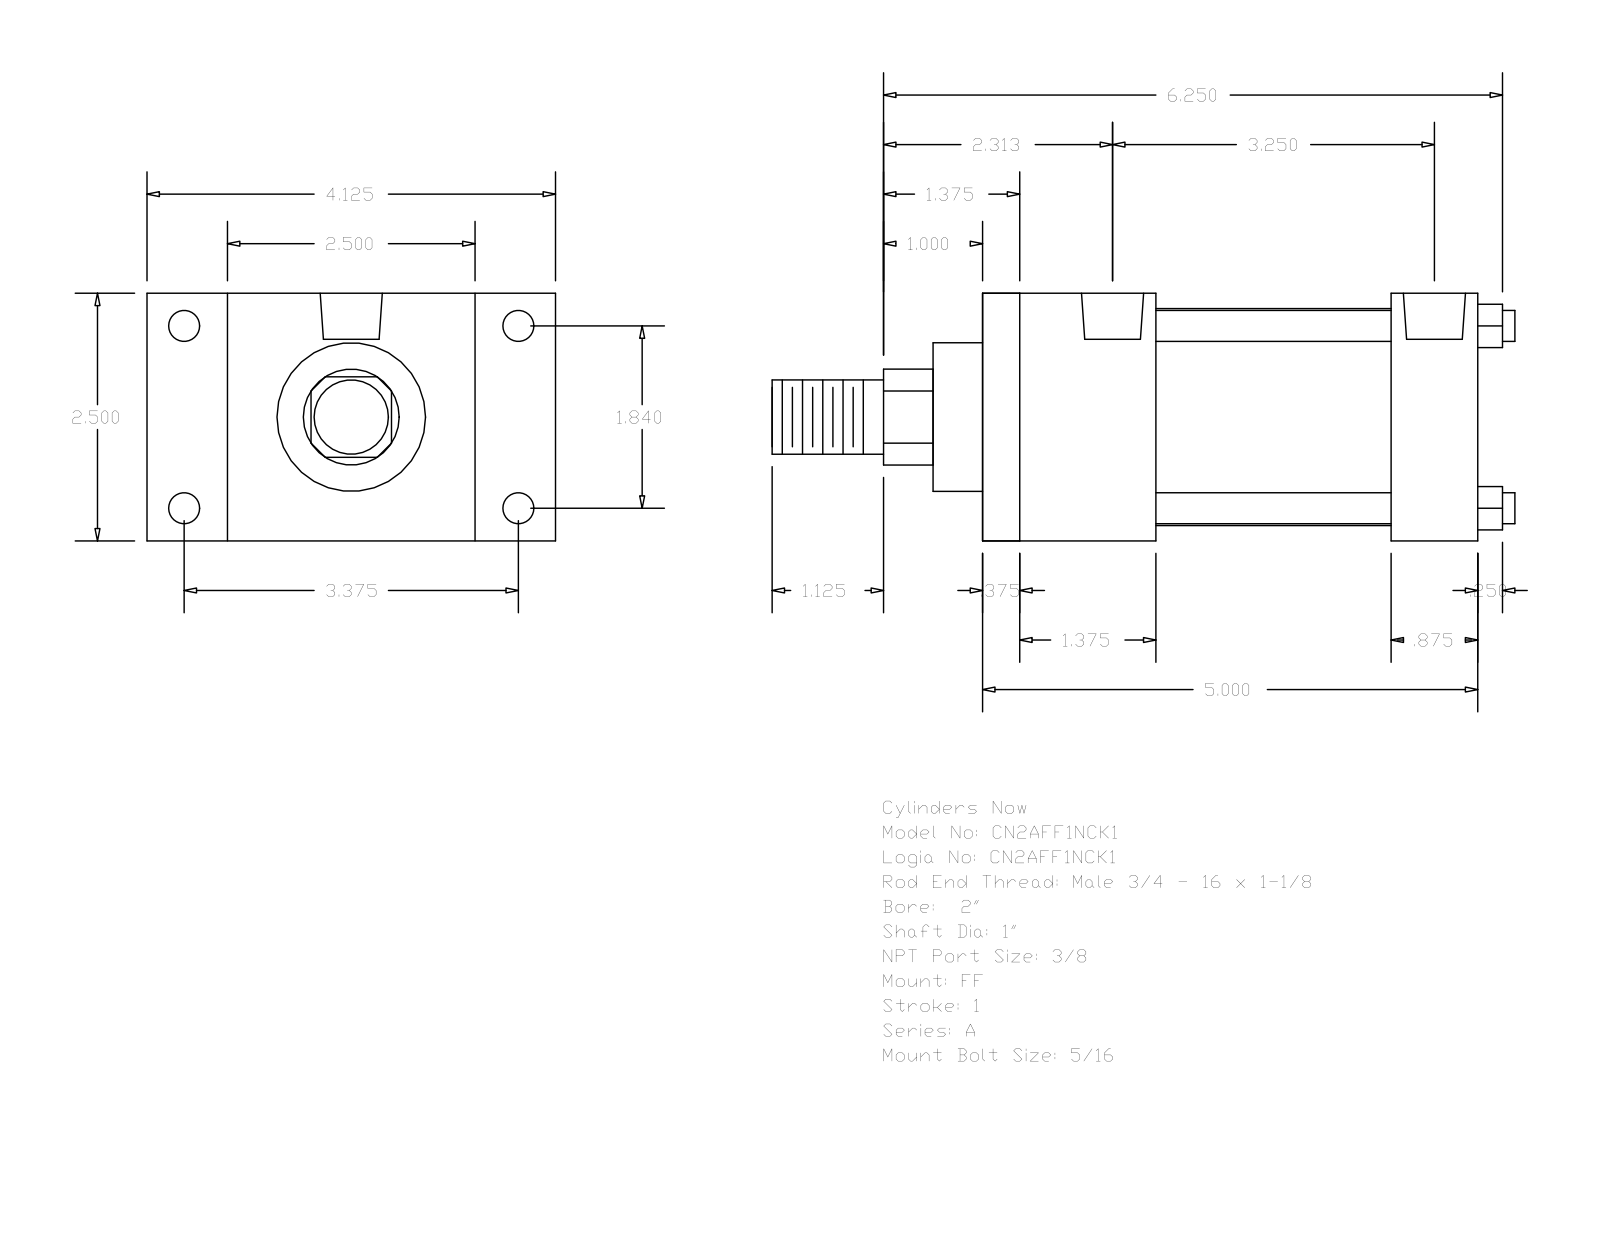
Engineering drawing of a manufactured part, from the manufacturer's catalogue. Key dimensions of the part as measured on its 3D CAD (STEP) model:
Part name (STEP PRODUCT): A_FF__0200_1
STEP written by: GSSL Pune (CONFIG_CONTROL_DESIGN)
Units: millimetres
Bodies: 0 solids, 92 faces (64 planar, 28 cylindrical, 0 other)
Overall size (bounding box): 190.5 × 104.78 × 63.5
Round holes (diameter × count): ⌀5.56 ×4, ⌀7.94 ×4, ⌀15.93 ×2
Round bosses / shafts (diameter × count): ⌀7.94 ×4, ⌀55.63 ×1, ⌀38.1 ×1, ⌀25.4 ×1, ⌀19.05 ×1
Partial cylindrical surfaces — rounded edges, fillets, slot ends (radius × count): R12.29 ×1
Main face-to-face distances: 63.5, 127, 117.48, 9.52, 22.22, 104.78, 20.64, 44.45, 34.93, 95.26
Hole centre spacings: 46.74, 76.98, 85.72, 97.63, 1.59, 3.98, 78.57, 80.96
